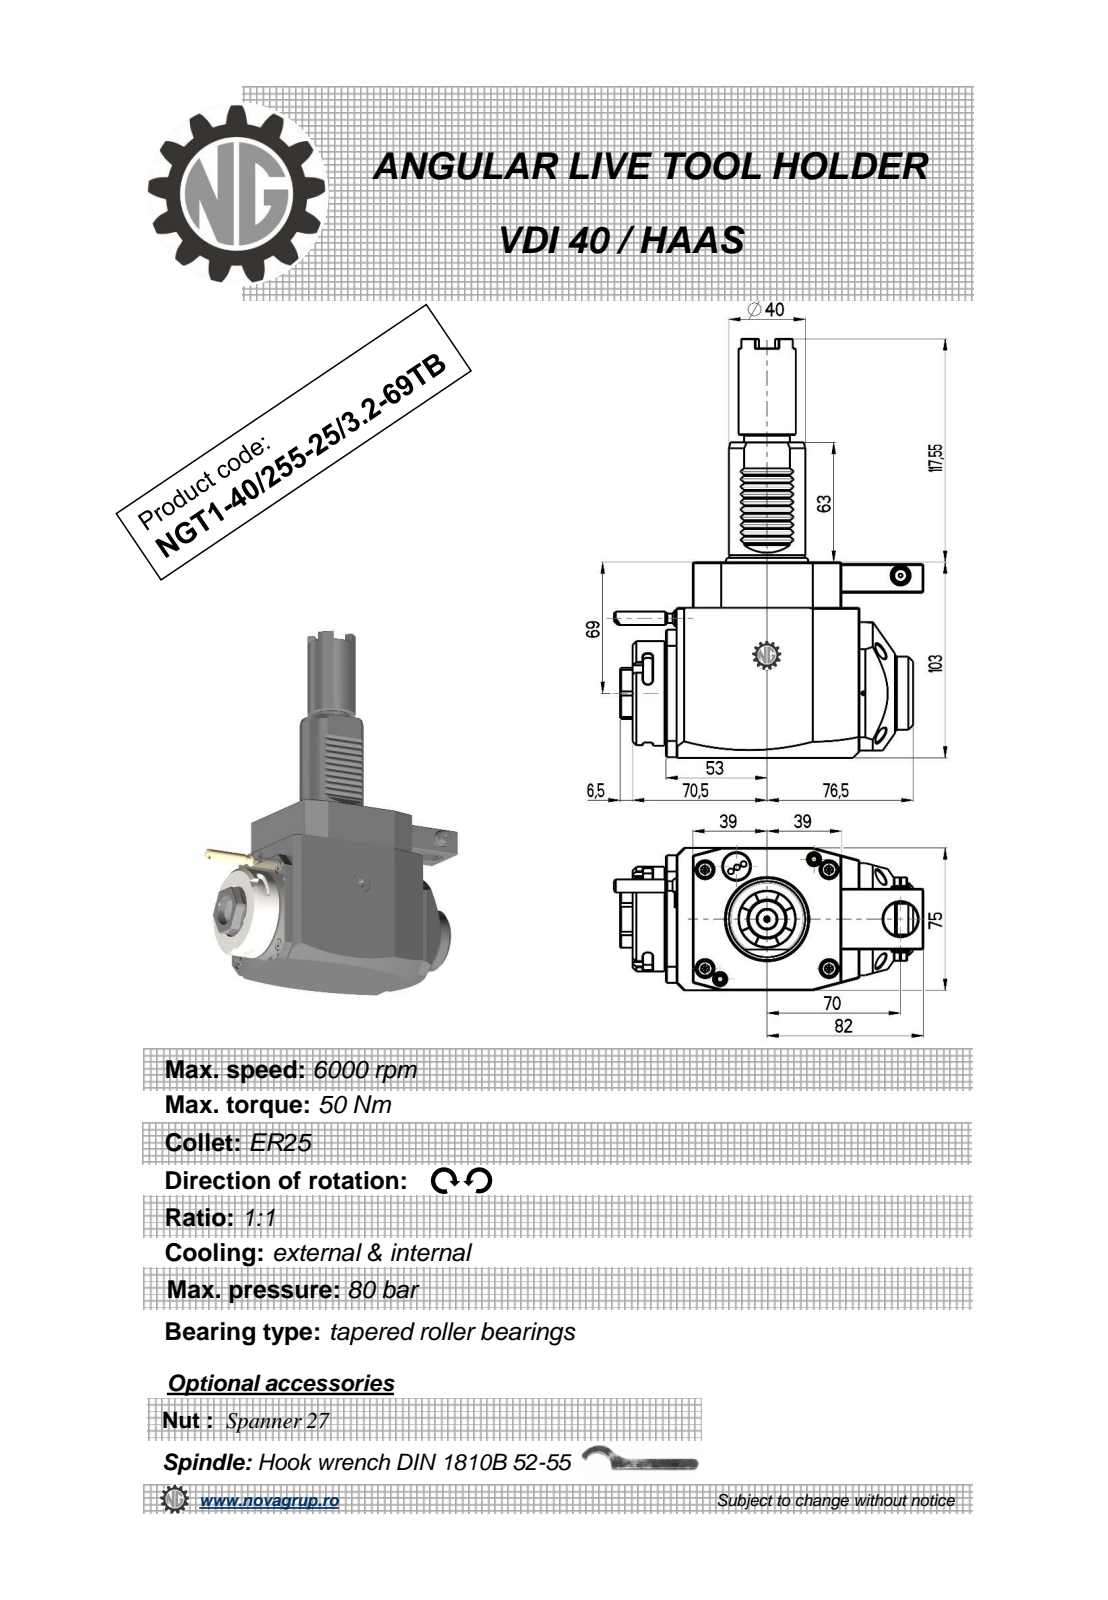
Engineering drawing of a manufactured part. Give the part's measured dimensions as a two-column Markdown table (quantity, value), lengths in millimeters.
| quantity | value |
| --- | --- |
| part name | NGT1_40_255_25_3_2_69TB |
| STEP written by | PRO/ENGINEER BY PARAMETRIC TECHNOLOGY CORPORATION, 2010280 (CONFIG_CONTROL_DESIGN) |
| units | millimeters |
| bodies | 1 solid, 397 faces (213 planar, 94 cylindrical, 90 other) |
| overall size | 220.55 × 162.33 × 75 |
| volume | 946 307 mm³ |
| surface area | 75 509 mm² |
| round holes (diameter × count) | 18 × 2, 2 × 1, 2.5 × 1, 3 × 1, 9.5 × 1, 20 × 1 |
| round bosses / shafts (diameter × count) | 8.96 × 2, 55 × 1, 48 × 1, 40 × 1, 38.5 × 1, 30 × 1, 24 × 1, 10 × 1 |
| partial cylindrical surfaces (radius × count) | 0.3 × 10, 2.5 × 6, 180 × 2, 0.5 × 1, 3.85 × 1, 4.25 × 1, 15 × 1, 24.5 × 1 |
| main face-to-face distances | 75, 103, 17.5, 23, 79, 102, 24, 31.5, 14, 87 |
| hole center spacings | 28.11, 43.2, 61.5, 70 |
